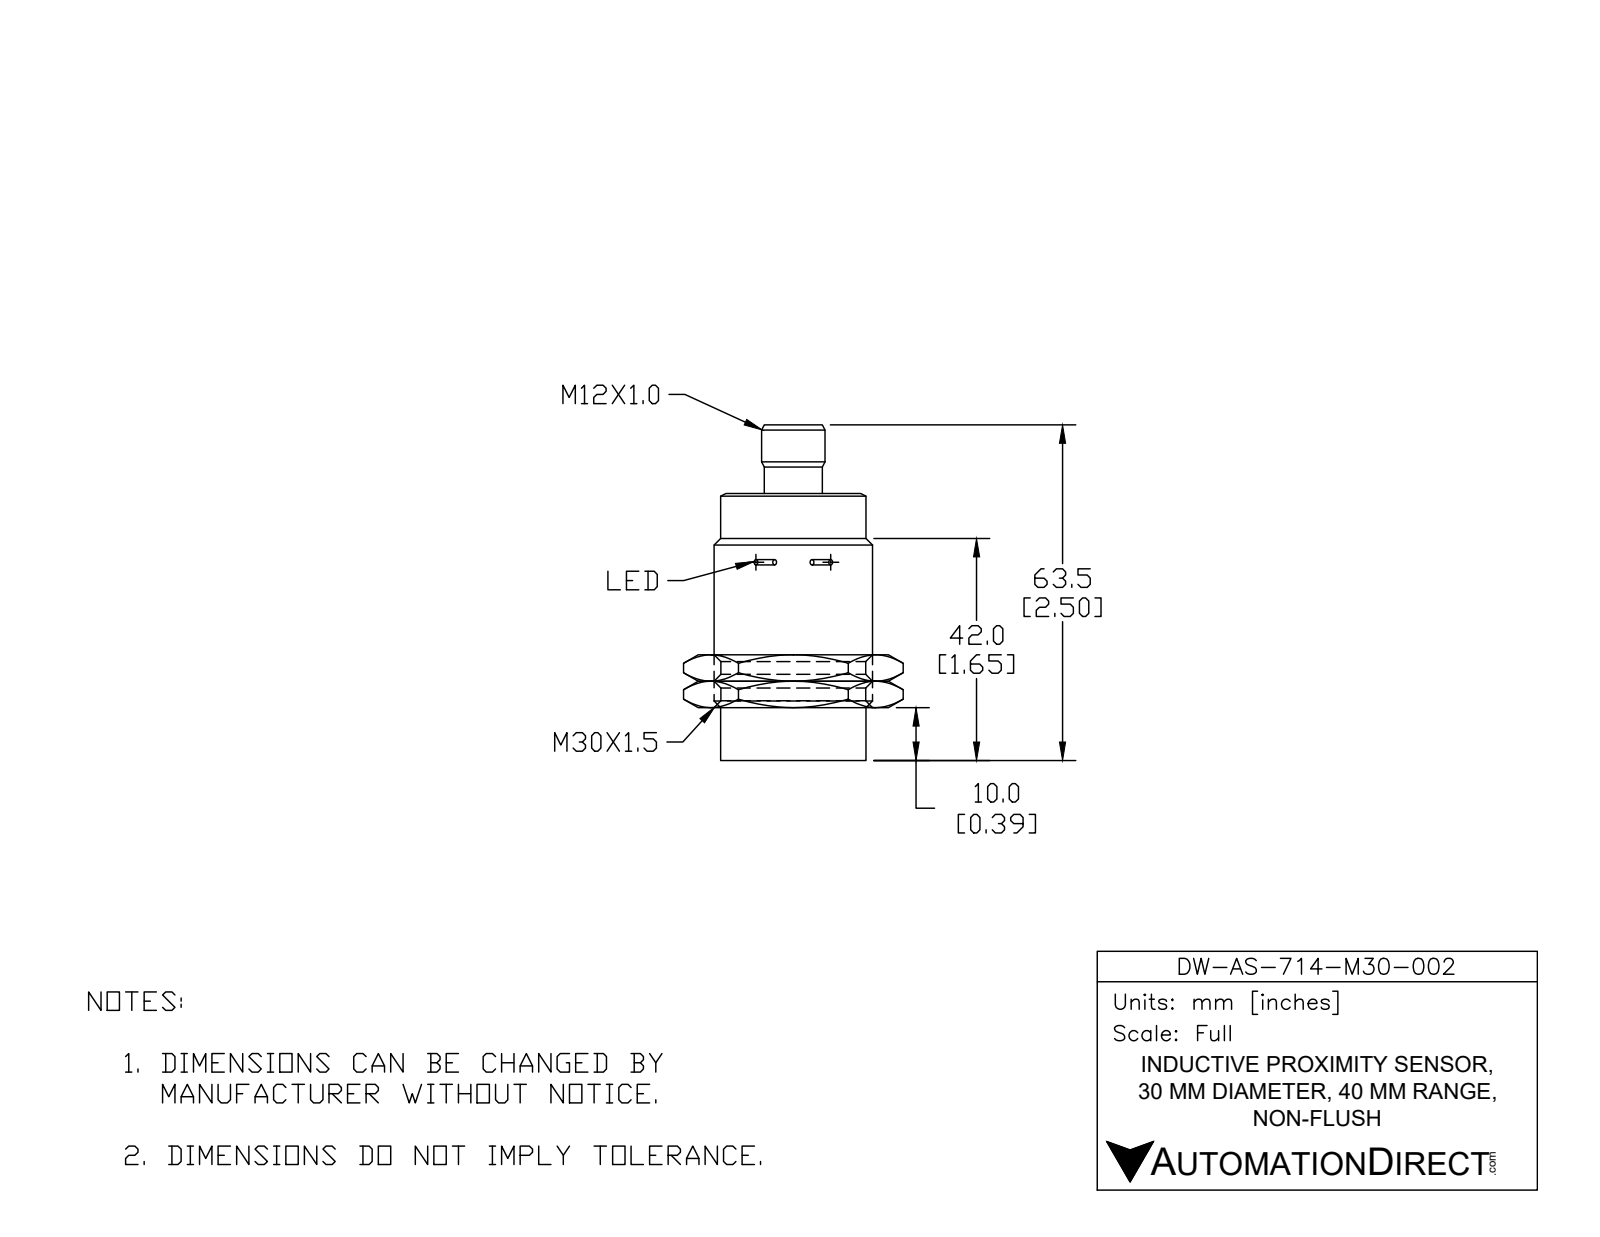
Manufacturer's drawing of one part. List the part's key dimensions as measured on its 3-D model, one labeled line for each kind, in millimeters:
Part name (STEP PRODUCT): DW-AS-714-M30-002
STEP written by: SolidWorks 2017 (AUTOMOTIVE_DESIGN)
Units: millimetres
Bodies: 1 solid, 51 faces (14 planar, 27 cylindrical, 10 other)
Overall size (bounding box): 63.6 × 30 × 30
Volume: 34 300 mm³ · Surface area: 6 923 mm²
Round holes (diameter × count): ⌀3 ×2, ⌀8.5 ×1
Round bosses / shafts (diameter × count): ⌀1.1 ×4, ⌀30 ×1, ⌀27.5 ×1, ⌀12 ×1, ⌀10.5 ×1
Partial cylindrical surfaces — rounded edges, fillets, slot ends (radius × count): R0.5 ×2, R0.6 ×1, R4.5 ×1, R4.9 ×1
Main face-to-face distances: 50.5, 54.8, 4.3, 42, 8.5, 12.9, 10, 32, 40.5, 44.9
